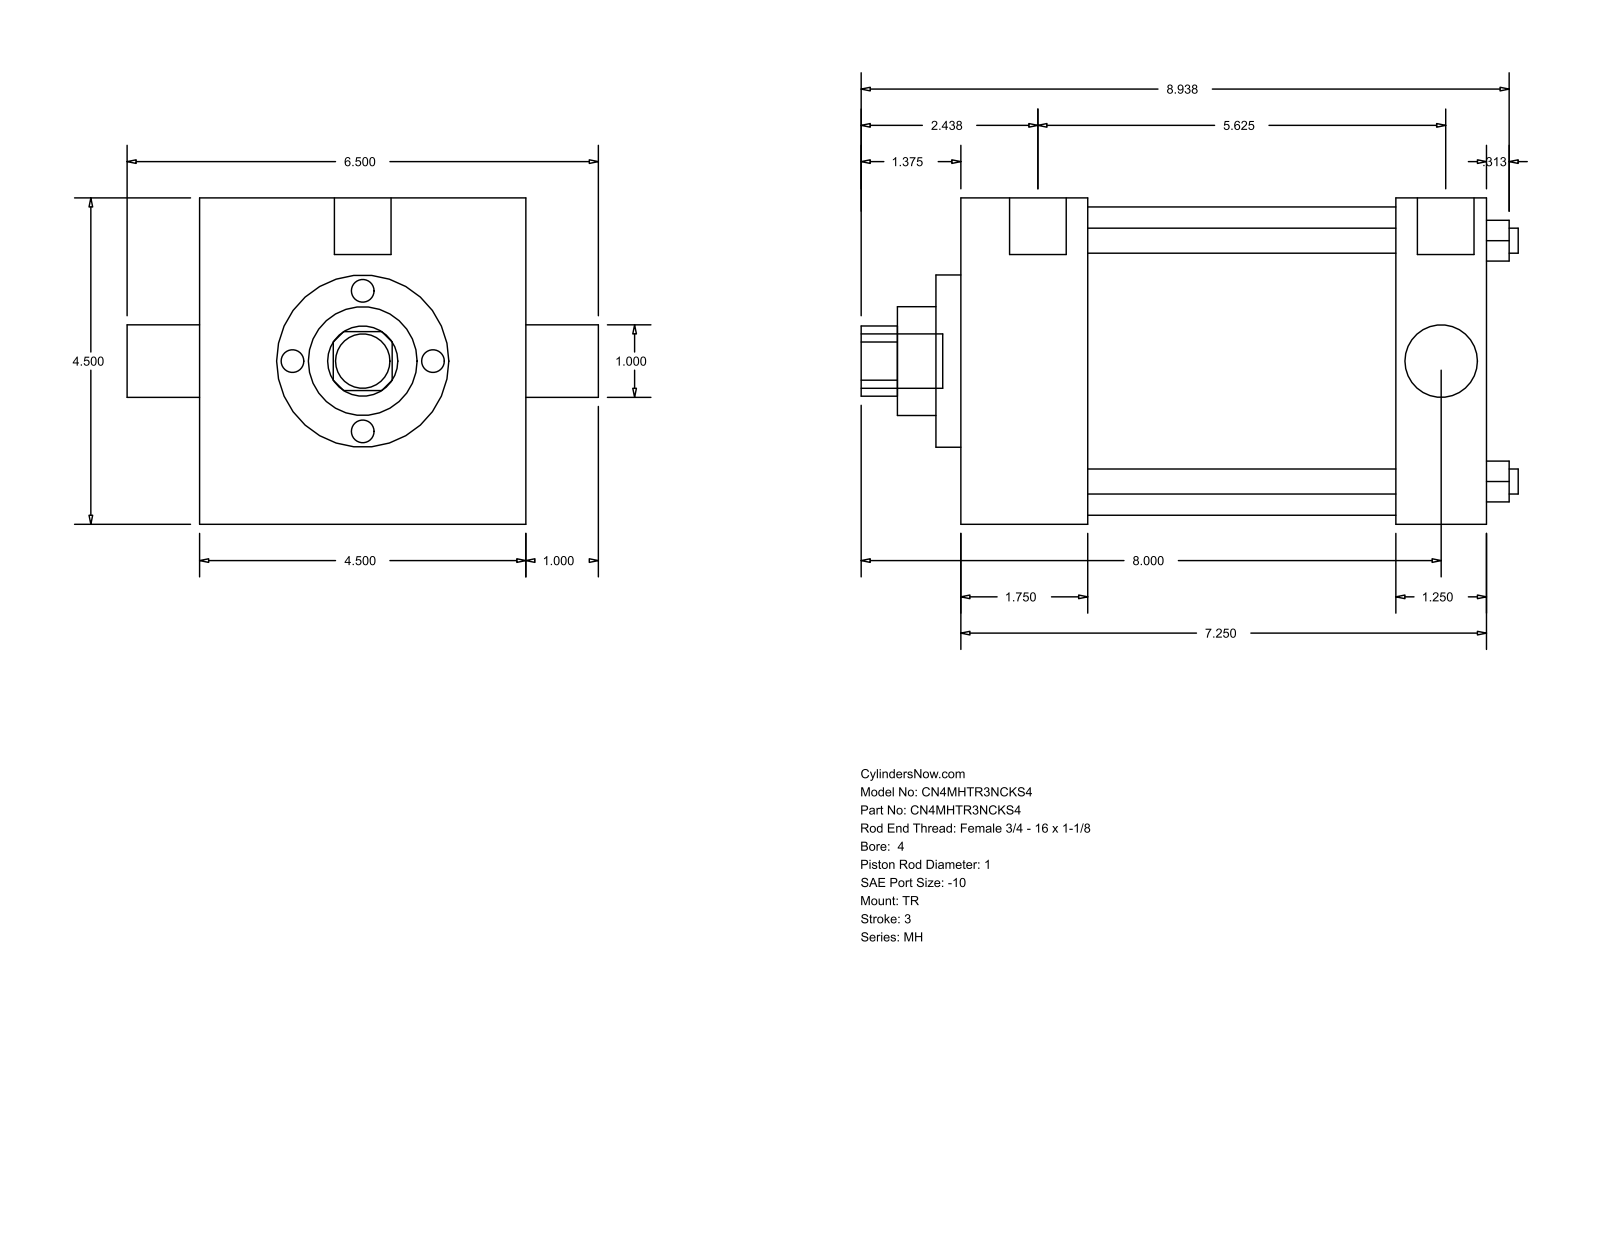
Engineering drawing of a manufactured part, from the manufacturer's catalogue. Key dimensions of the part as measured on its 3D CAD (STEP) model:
Part name (STEP PRODUCT): MH_TR__0400_1
STEP written by: GSSL Pune (CONFIG_CONTROL_DESIGN)
Units: millimetres
Bodies: 0 solids, 86 faces (61 planar, 25 cylindrical, 0 other)
Overall size (bounding box): 230.19 × 165.1 × 114.3
Round holes (diameter × count): ⌀8.76 ×4, ⌀25.4 ×2, ⌀38.1 ×1, ⌀60.33 ×1, ⌀107.95 ×1
Round bosses / shafts (diameter × count): ⌀8.73 ×3, ⌀19.84 ×2, ⌀19.05 ×1
Partial cylindrical surfaces — rounded edges, fillets, slot ends (radius × count): R12.29 ×1
Main face-to-face distances: 114.3, 184.15, 44.46, 139.69, 152.4, 107.94, 31.75, 8.73, 53.19, 161.13
Hole centre spacings: 59.62, 84.32, 119.25
